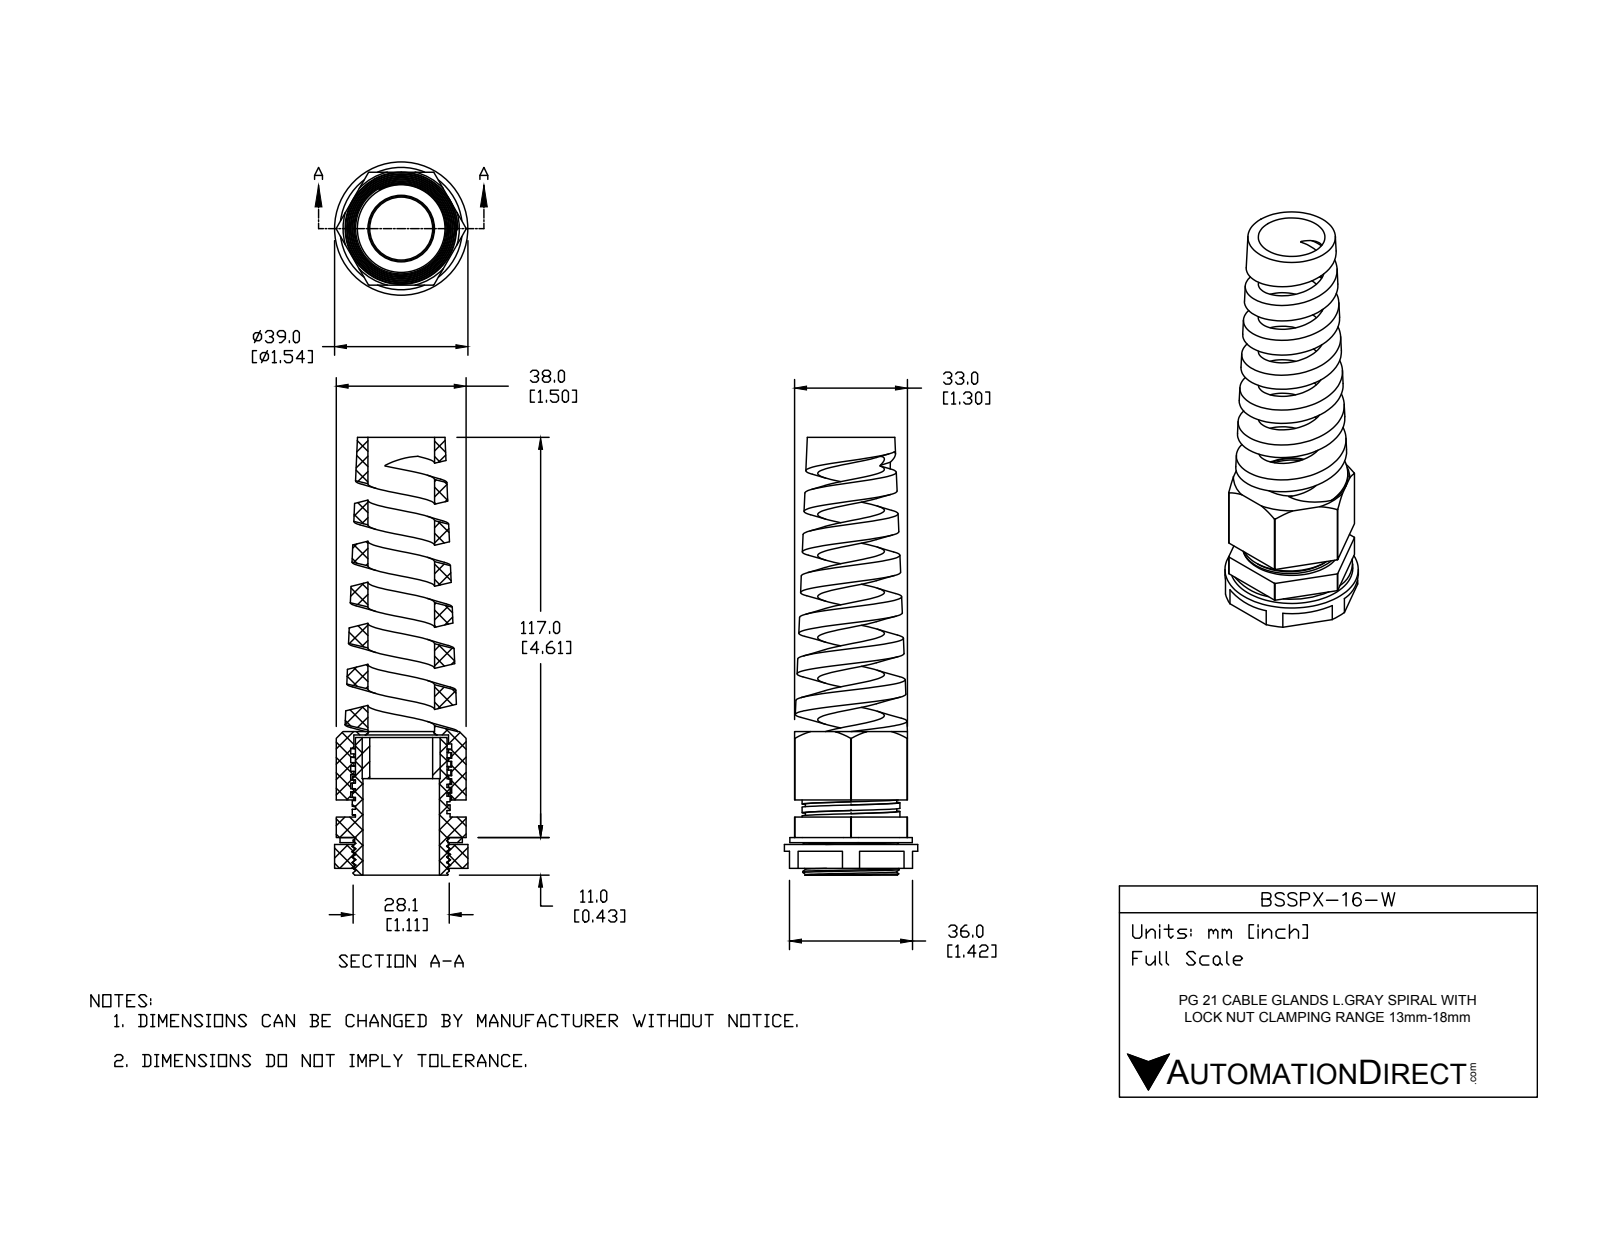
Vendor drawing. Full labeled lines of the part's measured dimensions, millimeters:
Part name (STEP PRODUCT): BSSPX-16-W
STEP written by: SolidWorks 2015 (CONFIG_CONTROL_DESIGN)
Units: millimetres
Bodies: 5 solids, 238 faces (105 planar, 94 cylindrical, 39 other)
Overall size (bounding box): 128 × 39 × 39
Volume: 38 563 mm³ · Surface area: 33 506 mm²
Round holes (diameter × count): ⌀18.4 ×1, ⌀19.5 ×1, ⌀22.4 ×1, ⌀22.8 ×1, ⌀27.2 ×1, ⌀27.34 ×1, ⌀27.67 ×1
Round bosses / shafts (diameter × count): ⌀39 ×1, ⌀35.8 ×1, ⌀28.6 ×1, ⌀28.1 ×1, ⌀26.8 ×1
Partial cylindrical surfaces — rounded edges, fillets, slot ends (radius × count): R19 ×1
Main face-to-face distances: 33, 1.5, 2, 7.5, 0.5, 9, 7, 20, 11, 34.5
